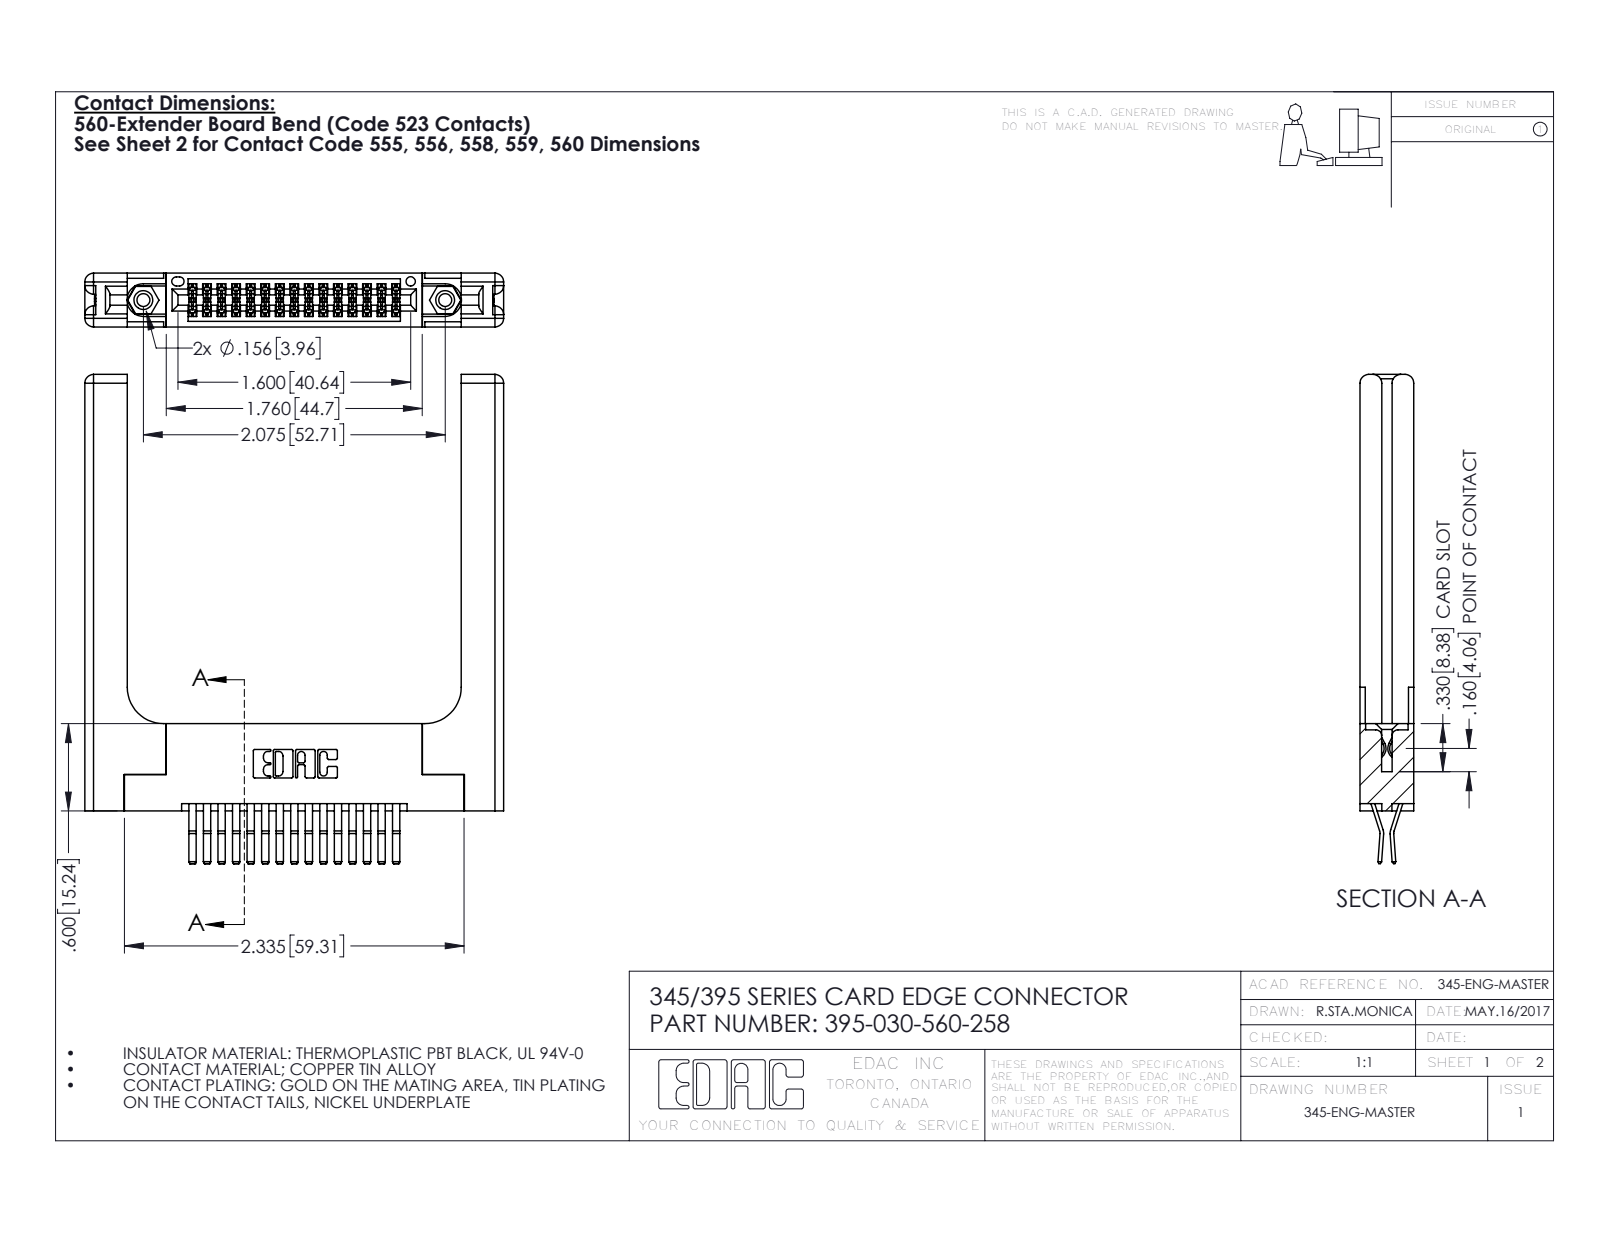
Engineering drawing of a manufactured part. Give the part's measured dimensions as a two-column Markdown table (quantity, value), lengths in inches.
| quantity | value |
| --- | --- |
| part name | 345-250-001_345-250-001-102; 345-220-058_345-220-058; 395-030-560-258; 345 Part_Flush Mounting Lugs - 0.156 Dia-TH (+1 more) |
| STEP written by | SolidWorks 2016 (CONFIG_CONTROL_DESIGN) |
| units | inches |
| bodies | 35 solids, 1942 faces (1218 planar, 664 cylindrical, 60 other) |
| overall size | 3.362 × 2.879 × 0.37 |
| volume | 0.947 in³ |
| surface area | 23.97 in² |
| round holes (diameter × count) | 0.089 × 2, 0.125 × 2, 0.156 × 2, 0.064 × 1 |
| round bosses / shafts (diameter × count) | 0.155 × 2 |
| partial cylindrical surfaces (radius × count) | 0.006 × 45, 0.01 × 22, 0.06 × 16, 0.007 × 6, 0.031 × 6, 0.026 × 3, 0.01 × 2, 0.014 × 2 |
| main face-to-face distances | 0.37, 0.072, 0.298, 0.025, 0.077, 0.148, 0.15, 0.22, 0.2, 0.225 |
| hole center spacings | 0.27, 1.842, 2.075 |
